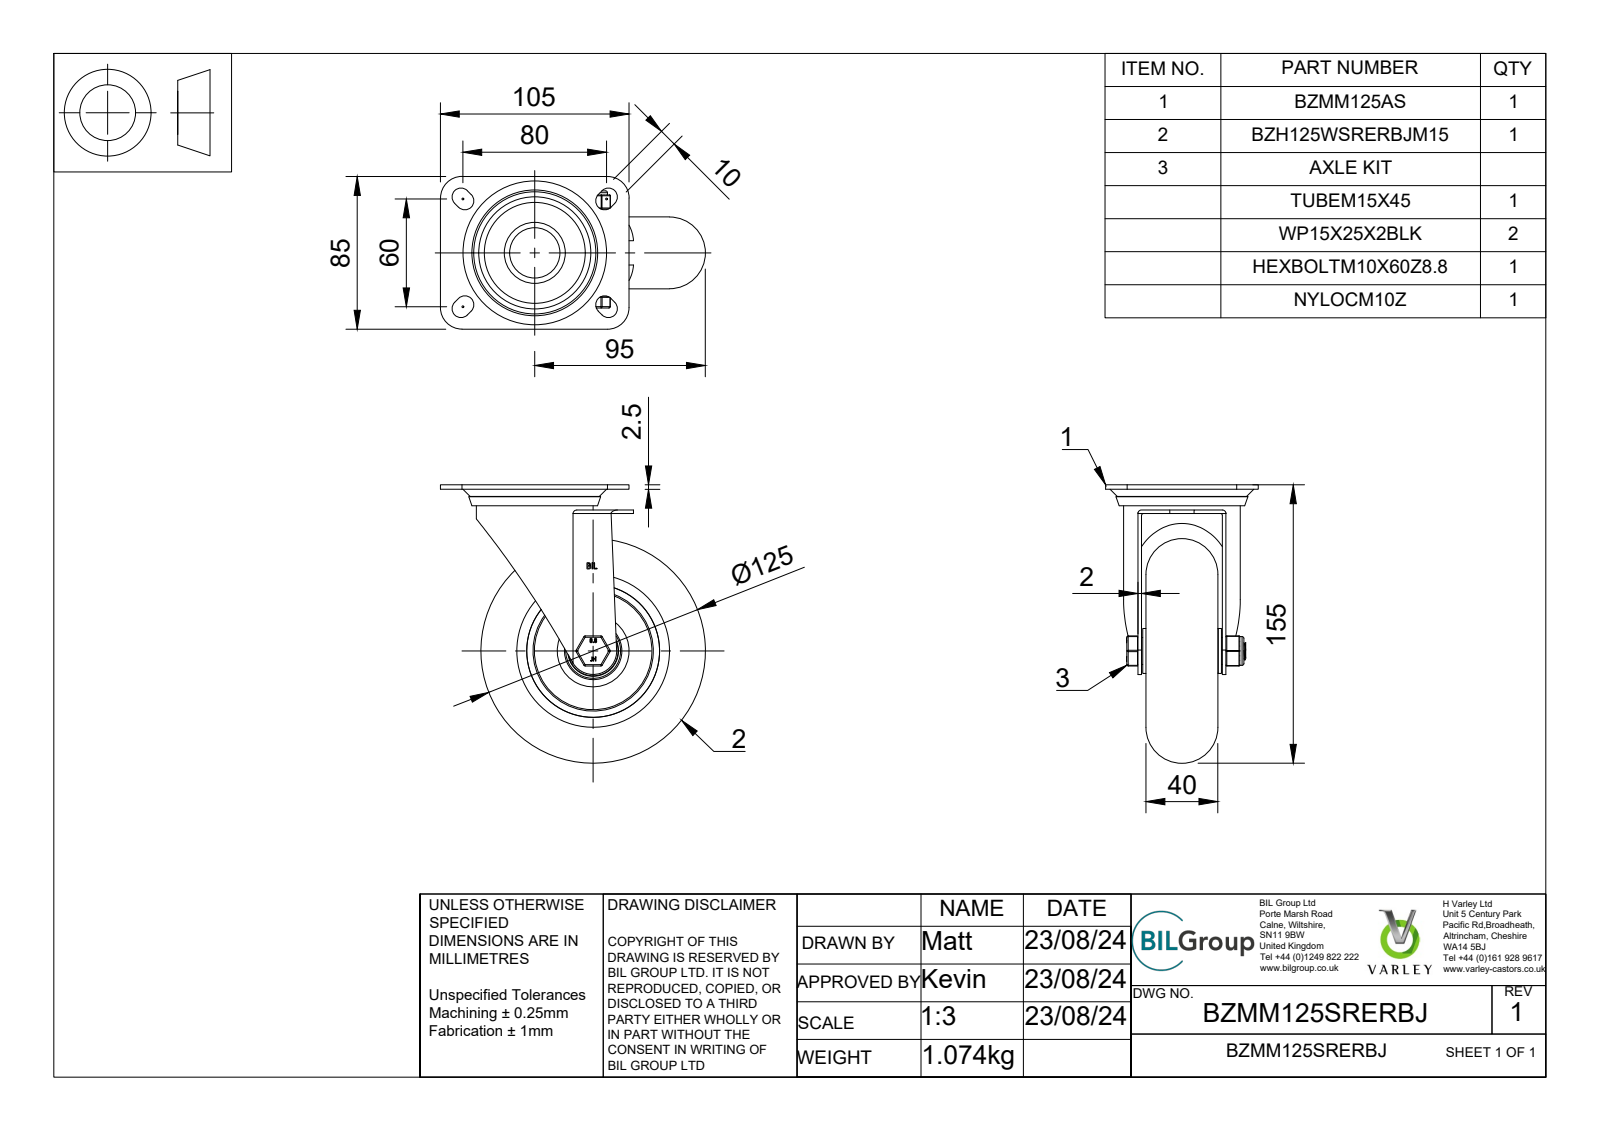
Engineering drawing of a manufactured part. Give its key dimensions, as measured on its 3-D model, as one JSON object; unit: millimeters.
{"part_name": "BZMM125SRERBJ v3; BZMM125AS - 2 v2; ZINC PLATED, PRESSED STEEL TOP PLATE; ZINC PLATED, PRESSED STEEL FORKS (+8 more)", "step_written_by": "Autodesk Translation Framework v13.14.0.145 (AUTOMOTIVE_DESIGN)", "units": "millimeters", "bodies": {"solids": 40, "faces": 1099, "planar": 381, "cylindrical": 195, "other": 523}, "overall_size": [155, 147.5, 85], "volume_mm3": 421891, "surface_area_mm2": 143209, "round_holes": [[28, 2], [10, 1], [10.2, 1], [10.3, 1], [12, 1], [15, 1], [15.75, 1], [20.5, 1], [26, 1], [26.8, 1], [28.2, 1], [32, 1]], "round_bosses_or_shafts": [[65, 1], [49, 1], [40, 1], [34, 1], [25, 1], [21.5, 1], [20, 1], [19, 1]], "partial_cylinders_radius": [[0.5, 18], [0.75, 12], [5, 8], [1, 4], [12, 4], [2, 2], [20.69, 2], [11.4, 1]], "face_to_face_distances": [2, 2.5, 4.5, 11.5, 44.5, 15.75, 24.25, 20.25, 28.75, 9]}
